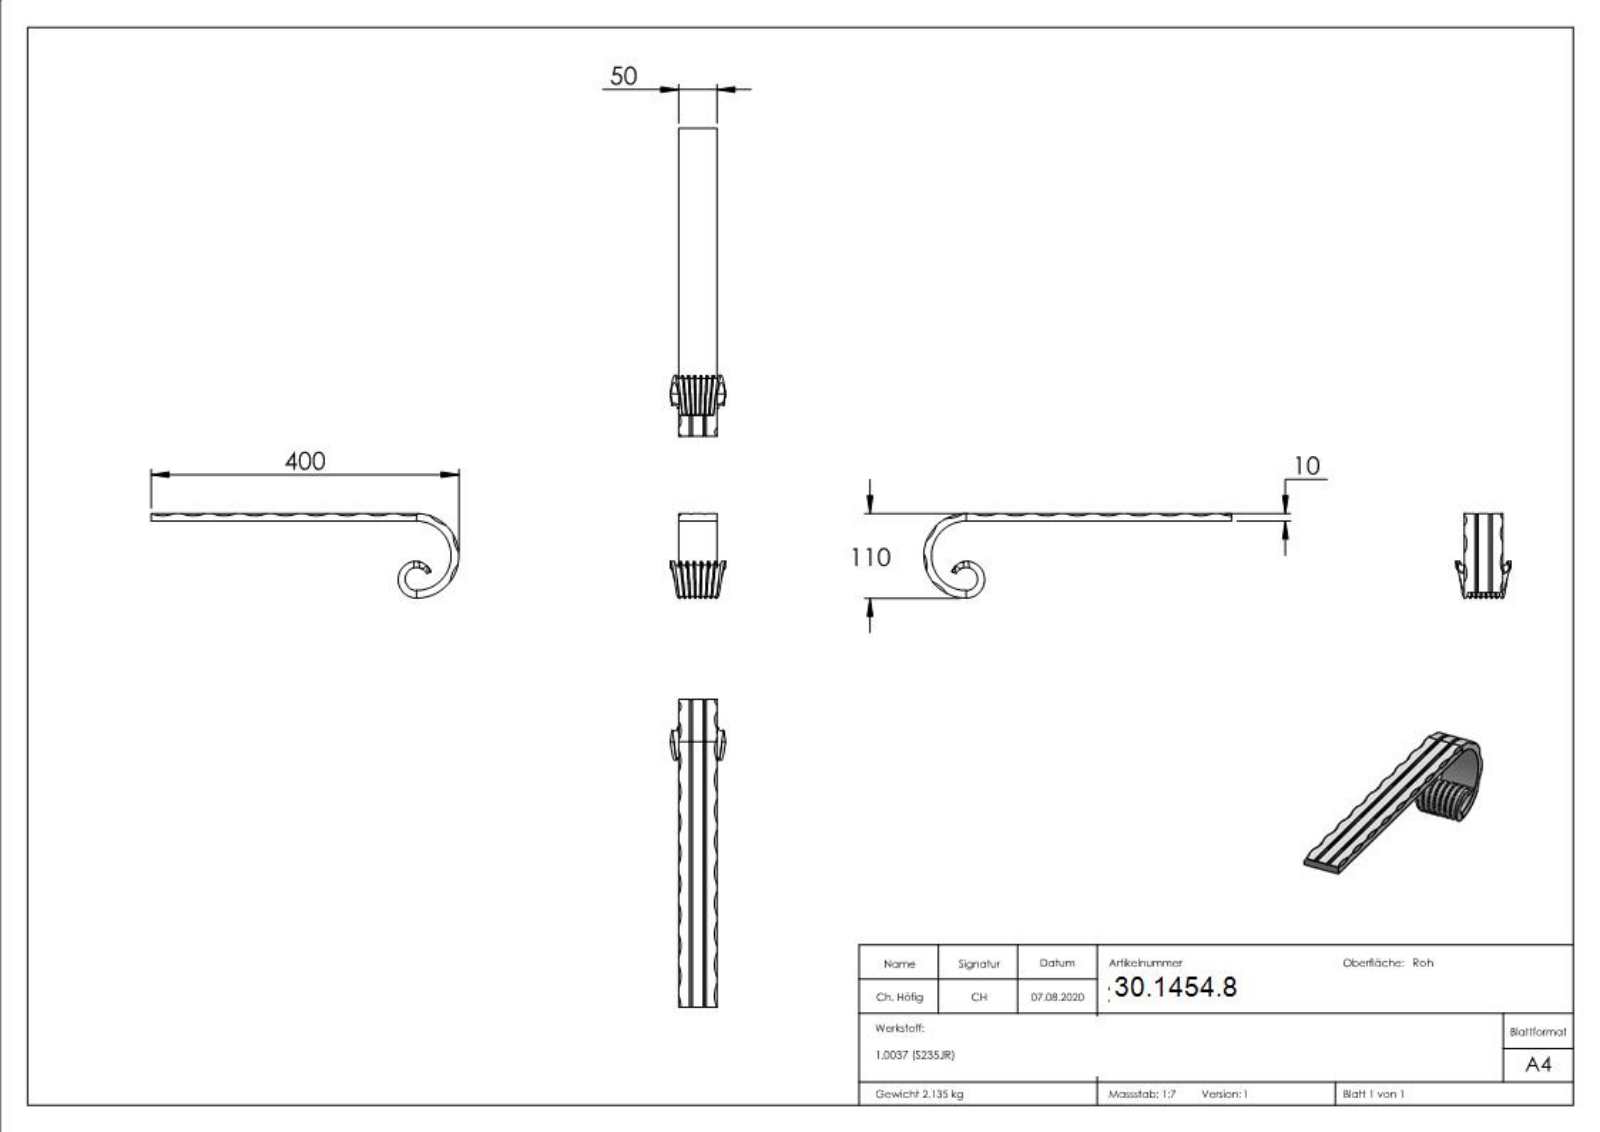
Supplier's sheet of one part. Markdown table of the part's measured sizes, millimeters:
| quantity | value |
| --- | --- |
| part name | 2160 |
| STEP written by | SolidWorks 2018 (CONFIG_CONTROL_DESIGN) |
| units | millimeters |
| bodies | 1 solid, 271 faces (92 planar, 6 cylindrical, 173 other) |
| overall size | 400 × 110 × 71.58 |
| volume | 273 689 mm³ |
| surface area | 75 402 mm² |
| partial cylindrical surfaces (radius × count) | 45 × 1, 55 × 1 |
| main face-to-face distances | 10, 50, 8.05, 2.97, 4.09, 0.39, 10.72, 4.48, 3.09, 7.45 |
